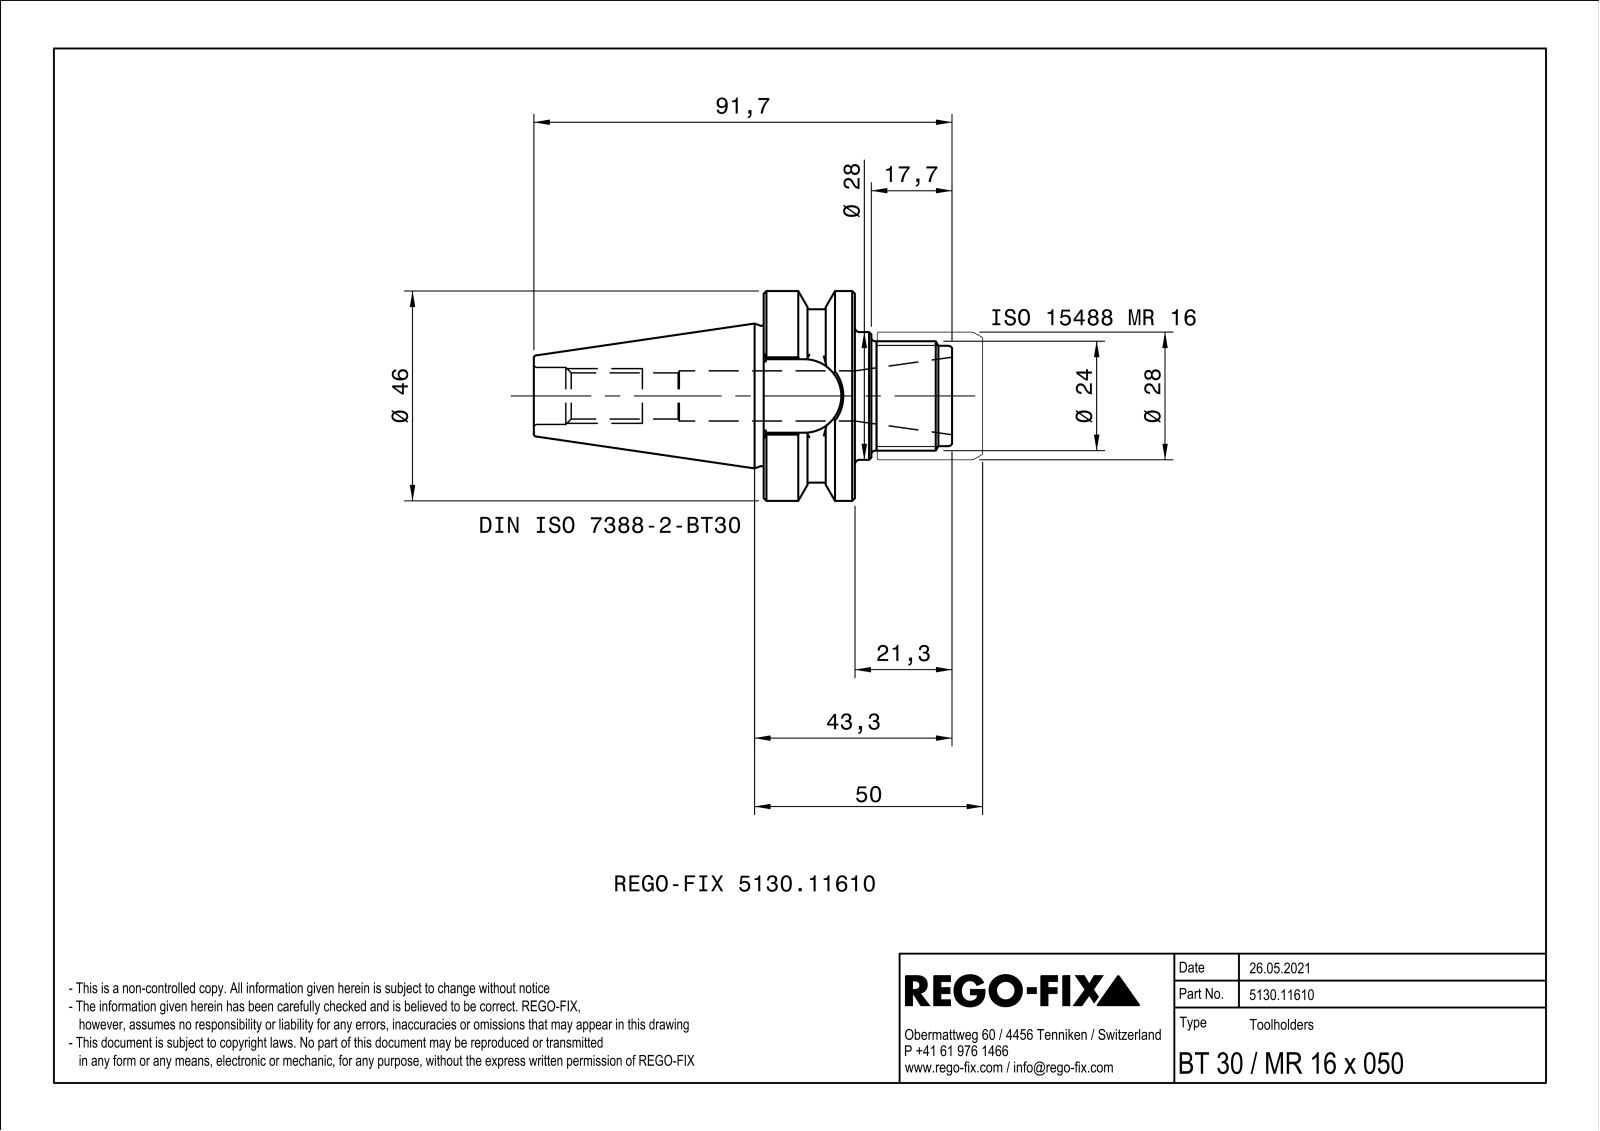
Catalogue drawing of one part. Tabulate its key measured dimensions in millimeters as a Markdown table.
| quantity | value |
| --- | --- |
| part name | NOCUT |
| STEP written by | SIEMENS PLM Software Solid Edge ST10 (AUTOMOTIVE_DESIGN) |
| units | millimeters |
| bodies | 1 solid, 89 faces (33 planar, 23 cylindrical, 33 other) |
| overall size | 91.7 × 46 × 46 |
| volume | 53 153 mm³ |
| surface area | 14 527 mm² |
| round holes (diameter × count) | 10.11 × 1, 11 × 1, 12.5 × 1 |
| round bosses / shafts (diameter × count) | 46 × 1, 28 × 1, 24 × 1, 22 × 1 |
| partial cylindrical surfaces (radius × count) | 0.5 × 8, 8.05 × 1, 19 × 1 |
| main face-to-face distances | 20, 32.5, 21.3, 41.3, 16.1, 91.7, 70.4, 50.4, 17.7, 3.6 |
